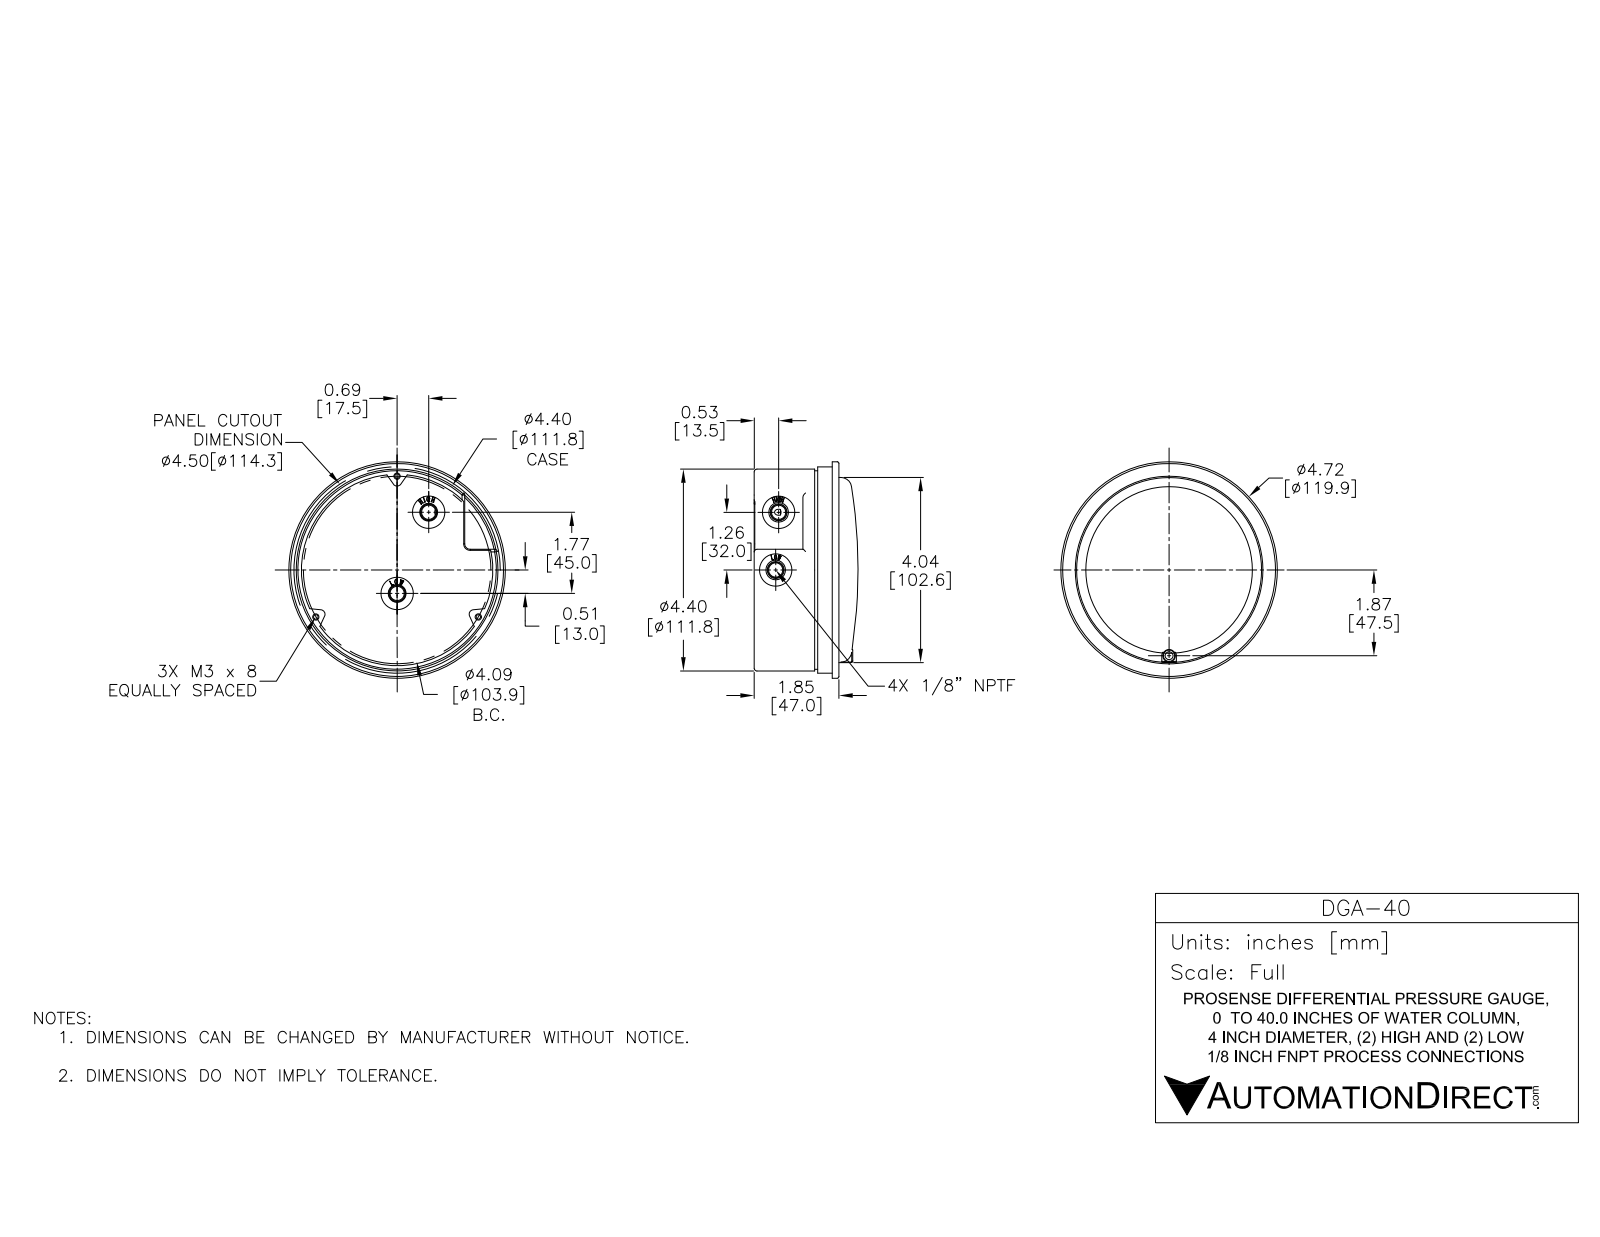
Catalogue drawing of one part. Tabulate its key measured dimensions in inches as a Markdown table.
| quantity | value |
| --- | --- |
| part name | DGA-01 |
| STEP written by | SolidWorks 2017 (AUTOMOTIVE_DESIGN) |
| units | inches |
| bodies | 2 solids, 404 faces (179 planar, 98 cylindrical, 127 other) |
| overall size | 4.72 × 4.72 × 2.277 |
| volume | 28.51 in³ |
| surface area | 95.36 in² |
| round holes (diameter × count) | 0.311 × 4, 0.705 × 4, 0.1 × 2, 0.1 × 1, 4.172 × 1 |
| round bosses / shafts (diameter × count) | 0.15 × 2, 0.125 × 2, 0.05 × 2, 4.72 × 1, 4.499 × 1, 4.4 × 1, 4.326 × 1, 4.038 × 1 |
| partial cylindrical surfaces (radius × count) | 0.015 × 13, 0.01 × 4, 0.05 × 4, 2.169 × 2, 0.098 × 1, 0.099 × 1, 0.1 × 1, 0.136 × 1 |
| main face-to-face distances | 1.818, 1.671, 0.146, 1.355, 0.317, 0.463, 0.031, 1.819, 0.464, 0.148 |
| hole center spacings | 1.844, 2.046, 3.546, 0.511, 1.045, 1.259, 1.436, 1.9 |
